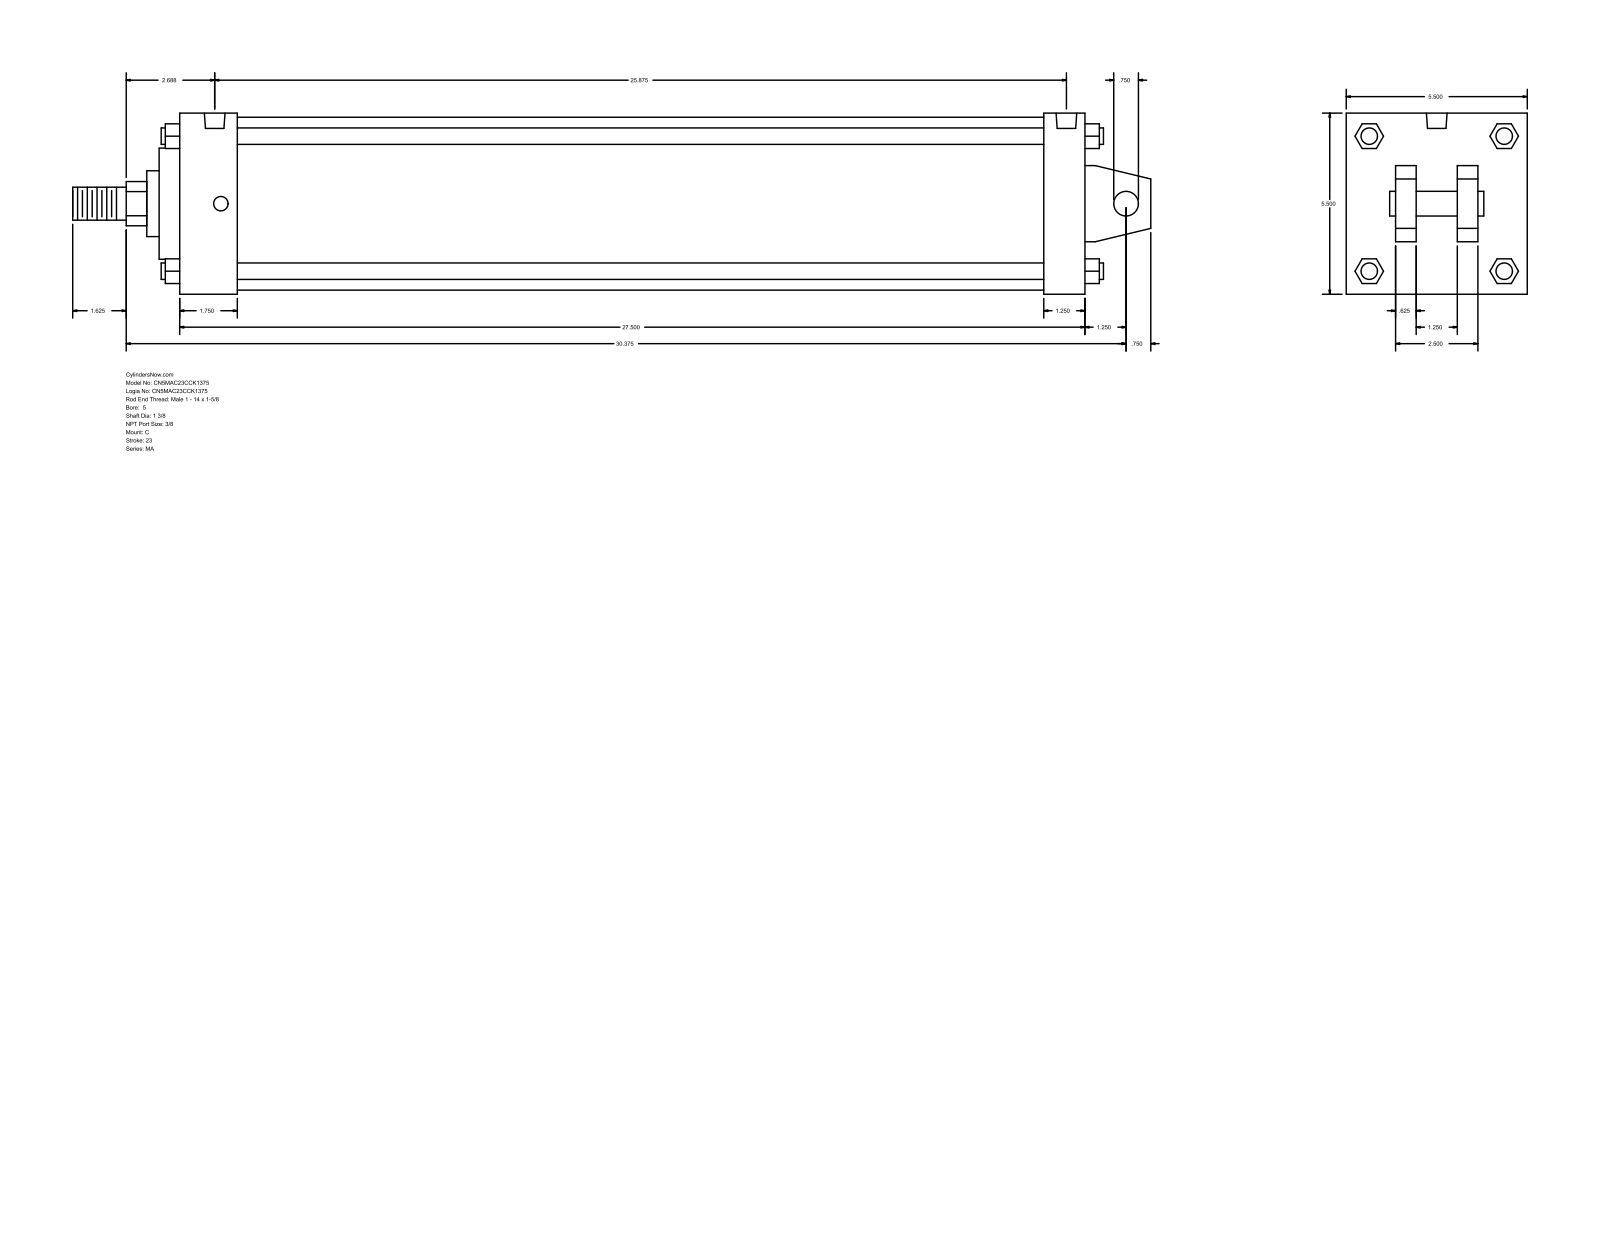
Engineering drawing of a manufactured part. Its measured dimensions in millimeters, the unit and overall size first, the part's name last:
Units: millimetres
Overall size (bounding box): 831.85 × 139.7 × 139.7
Round holes (diameter × count): ⌀11.11 ×4, ⌀15.93 ×2
Round bosses / shafts (diameter × count): ⌀12.7 ×4, ⌀133.35 ×1, ⌀85.72 ×1, ⌀50.8 ×1, ⌀34.92 ×1, ⌀25.4 ×1, ⌀19.05 ×1
Partial cylindrical surfaces — rounded edges, fillets, slot ends (radius × count): R17.06 ×1
Main face-to-face distances: 139.7, 698.5, 15.87, 666.75, 31.75, 44.45, 622.3, 654.05, 53.97, 38.1
Hole centre spacings: 647.7, 4.76, 4.77, 652.46, 652.47, 657.23
Bodies: 0 solids, 141 faces (109 planar, 32 cylindrical, 0 other)
Part name (STEP PRODUCT): MA_C__0500_1.375
STEP written by: GSSL Pune (CONFIG_CONTROL_DESIGN)
